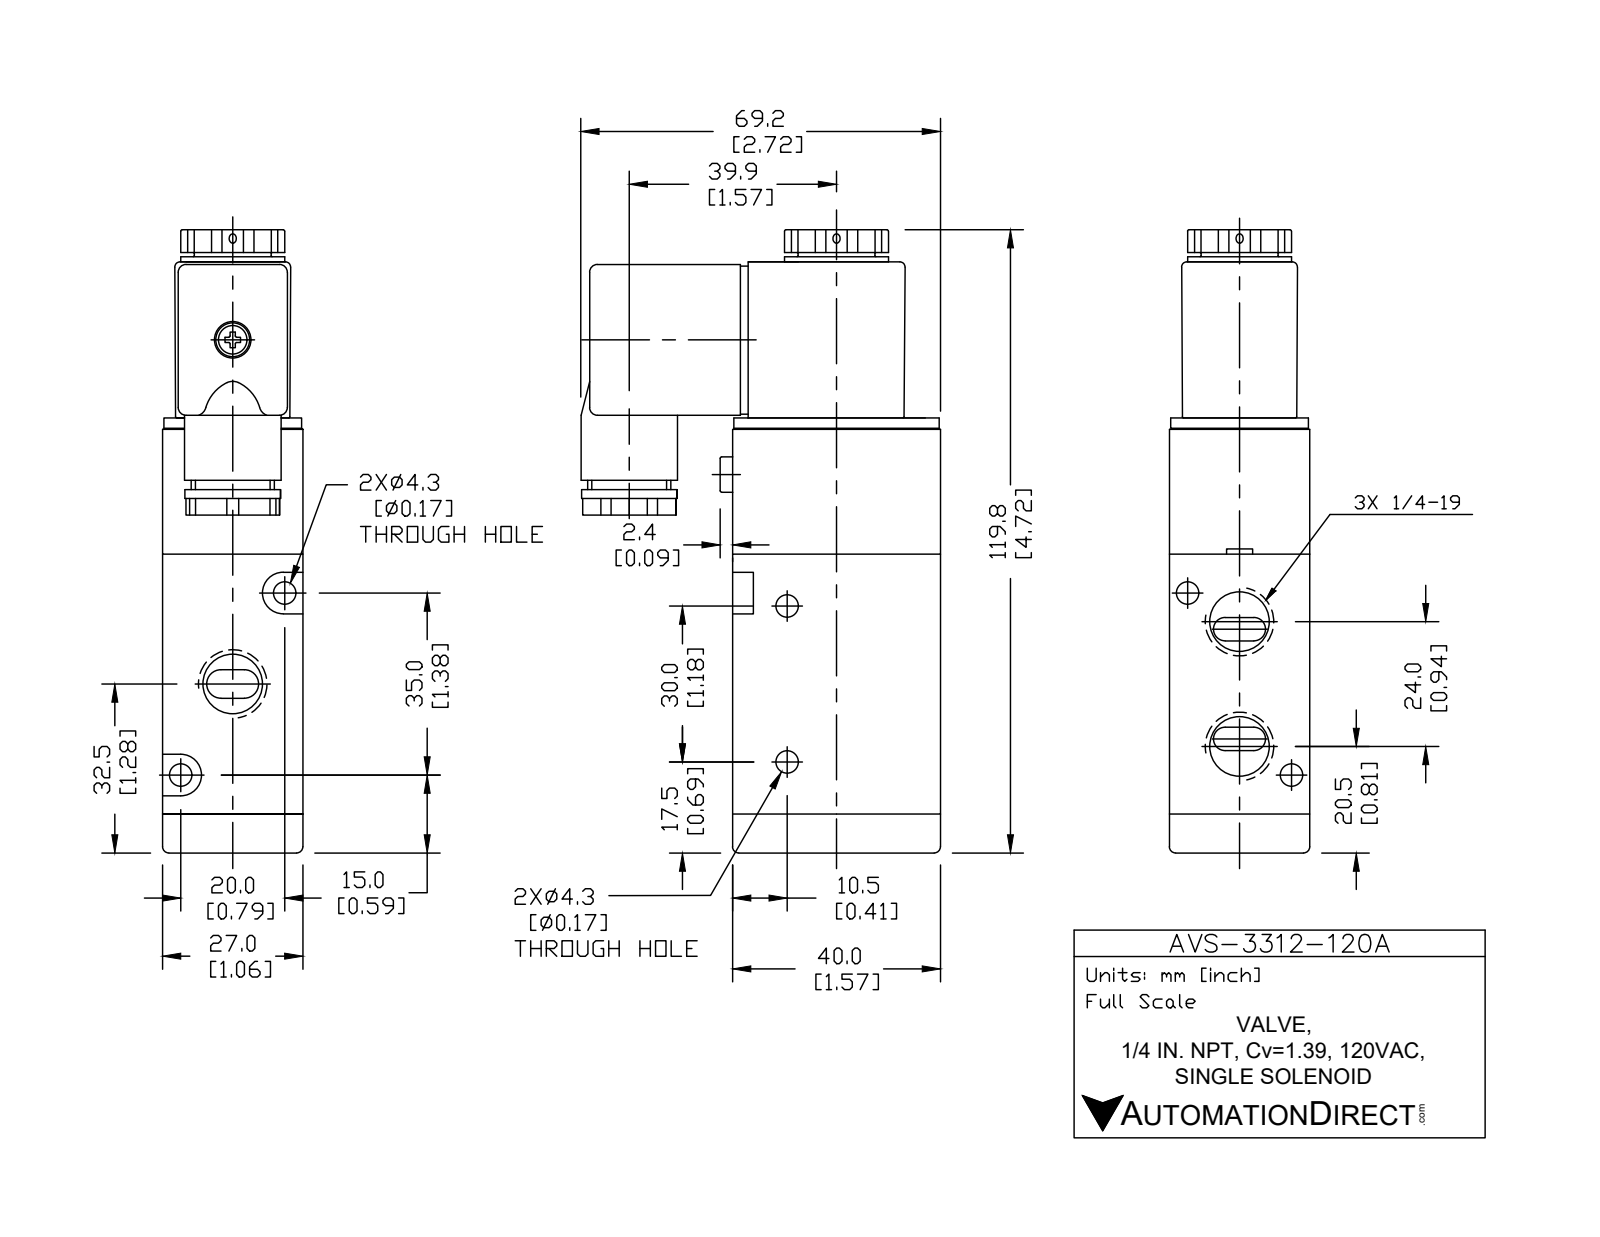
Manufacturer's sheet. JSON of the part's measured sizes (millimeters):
{"part_name": "AVS-3312-120A", "step_written_by": "SolidWorks 2015 (CONFIG_CONTROL_DESIGN)", "units": "millimeters", "bodies": {"solids": 4, "faces": 156, "planar": 81, "cylindrical": 53, "other": 22}, "overall_size": [119.9, 69.1, 27], "volume_mm3": 127198, "surface_area_mm2": 29011, "round_holes": [[4.3, 4], [11.13, 3], [9.3, 1]], "round_bosses_or_shafts": [[20, 1], [18.6, 1], [18.4, 1], [16, 1], [14.8, 1], [6.8, 1]], "partial_cylinders_radius": [[0.5, 11], [1, 10], [4, 2]], "face_to_face_distances": [50, 27, 3, 24, 7.5, 57.5, 40, 21, 2.26, 2.27], "hole_center_spacings": [11.41, 12.09, 31.15, 19.46, 20.94, 24, 30, 40.31]}
